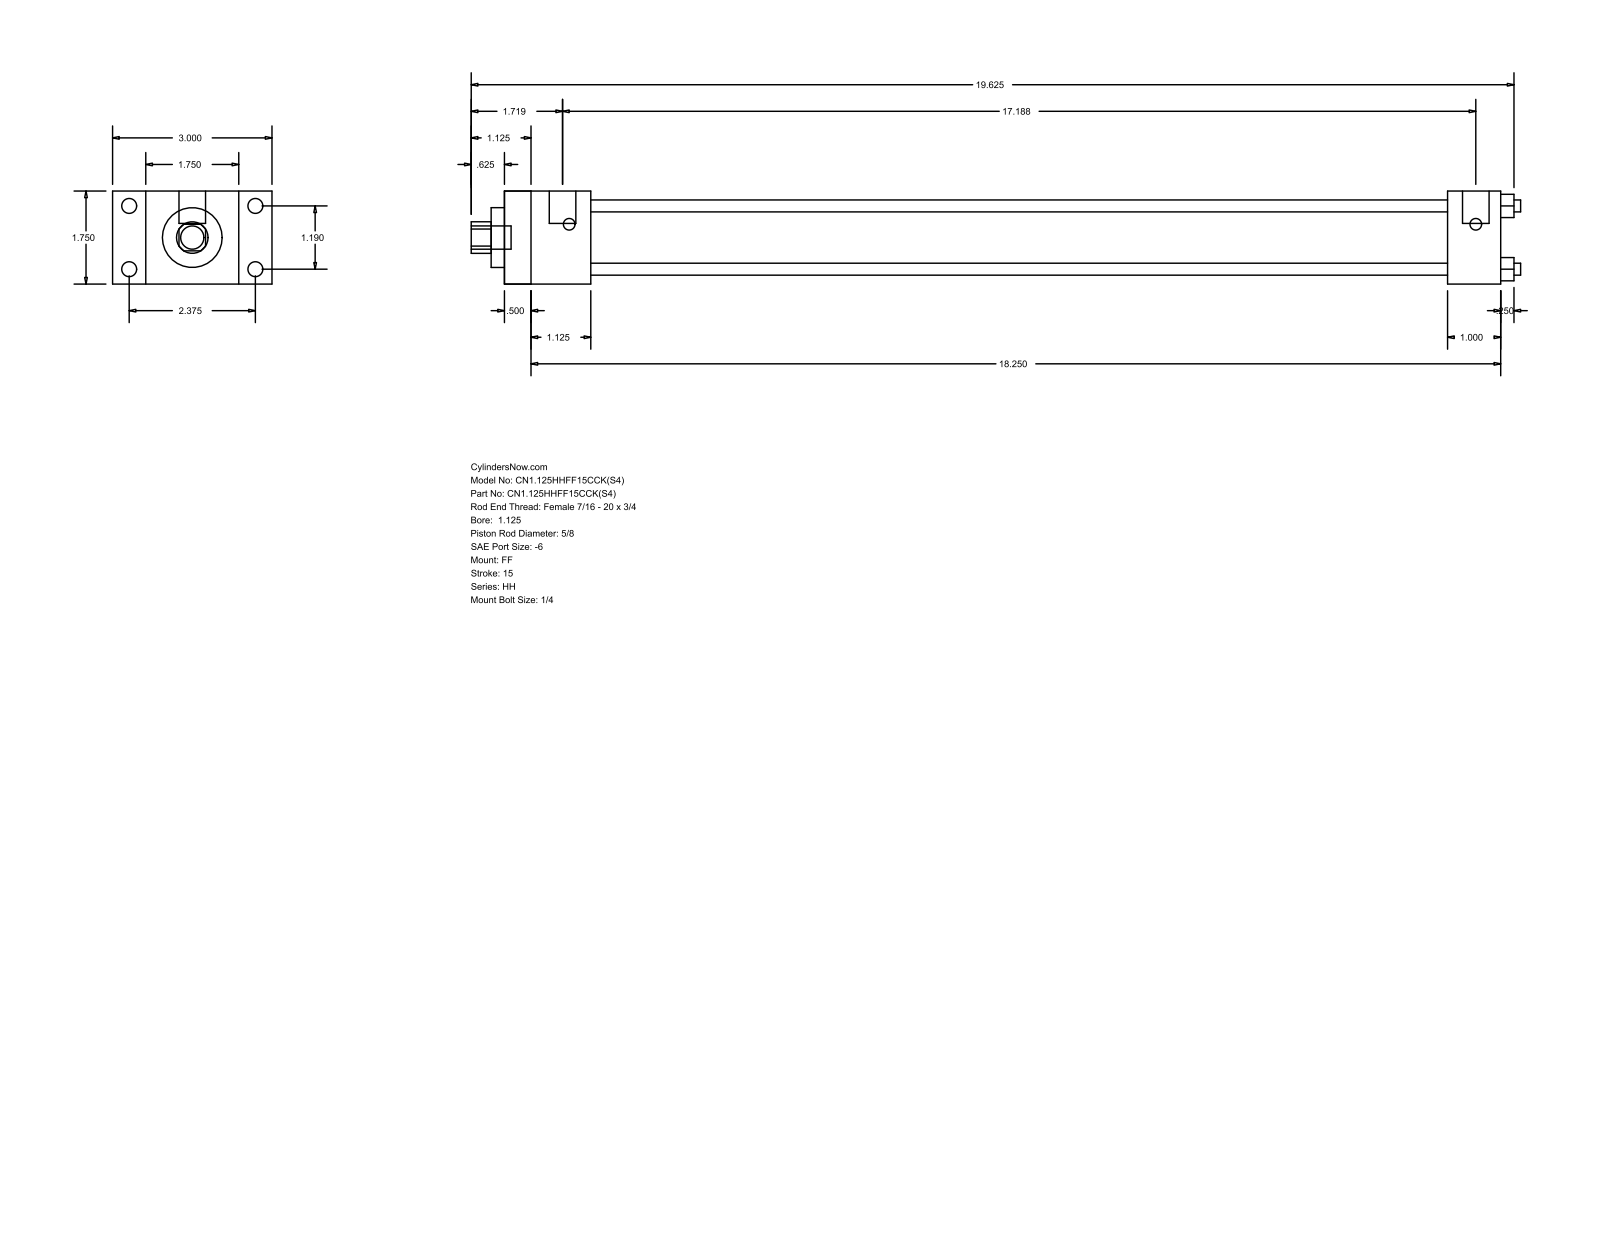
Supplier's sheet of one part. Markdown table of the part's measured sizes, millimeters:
| quantity | value |
| --- | --- |
| part name | HH_FF__0112_0.625 |
| STEP written by | GSSL Pune (CONFIG_CONTROL_DESIGN) |
| units | millimeters |
| bodies | 0 solids, 92 faces (64 planar, 28 cylindrical, 0 other) |
| overall size | 501.65 × 76.2 × 44.45 |
| round holes (diameter × count) | 5.71 × 4, 15.88 × 1, 28.57 × 1, 34.92 × 1 |
| round bosses / shafts (diameter × count) | 7.14 × 4, 5.56 × 4, 12.7 × 2, 11.11 × 1 |
| partial cylindrical surfaces (radius × count) | 7.54 × 1 |
| main face-to-face distances | 44.46, 476.24, 12.69, 463.55, 15.87, 60.33, 28.58, 41.27, 450.85, 438.16 |
| hole center spacings | 21.37, 30.22, 42.74 |
